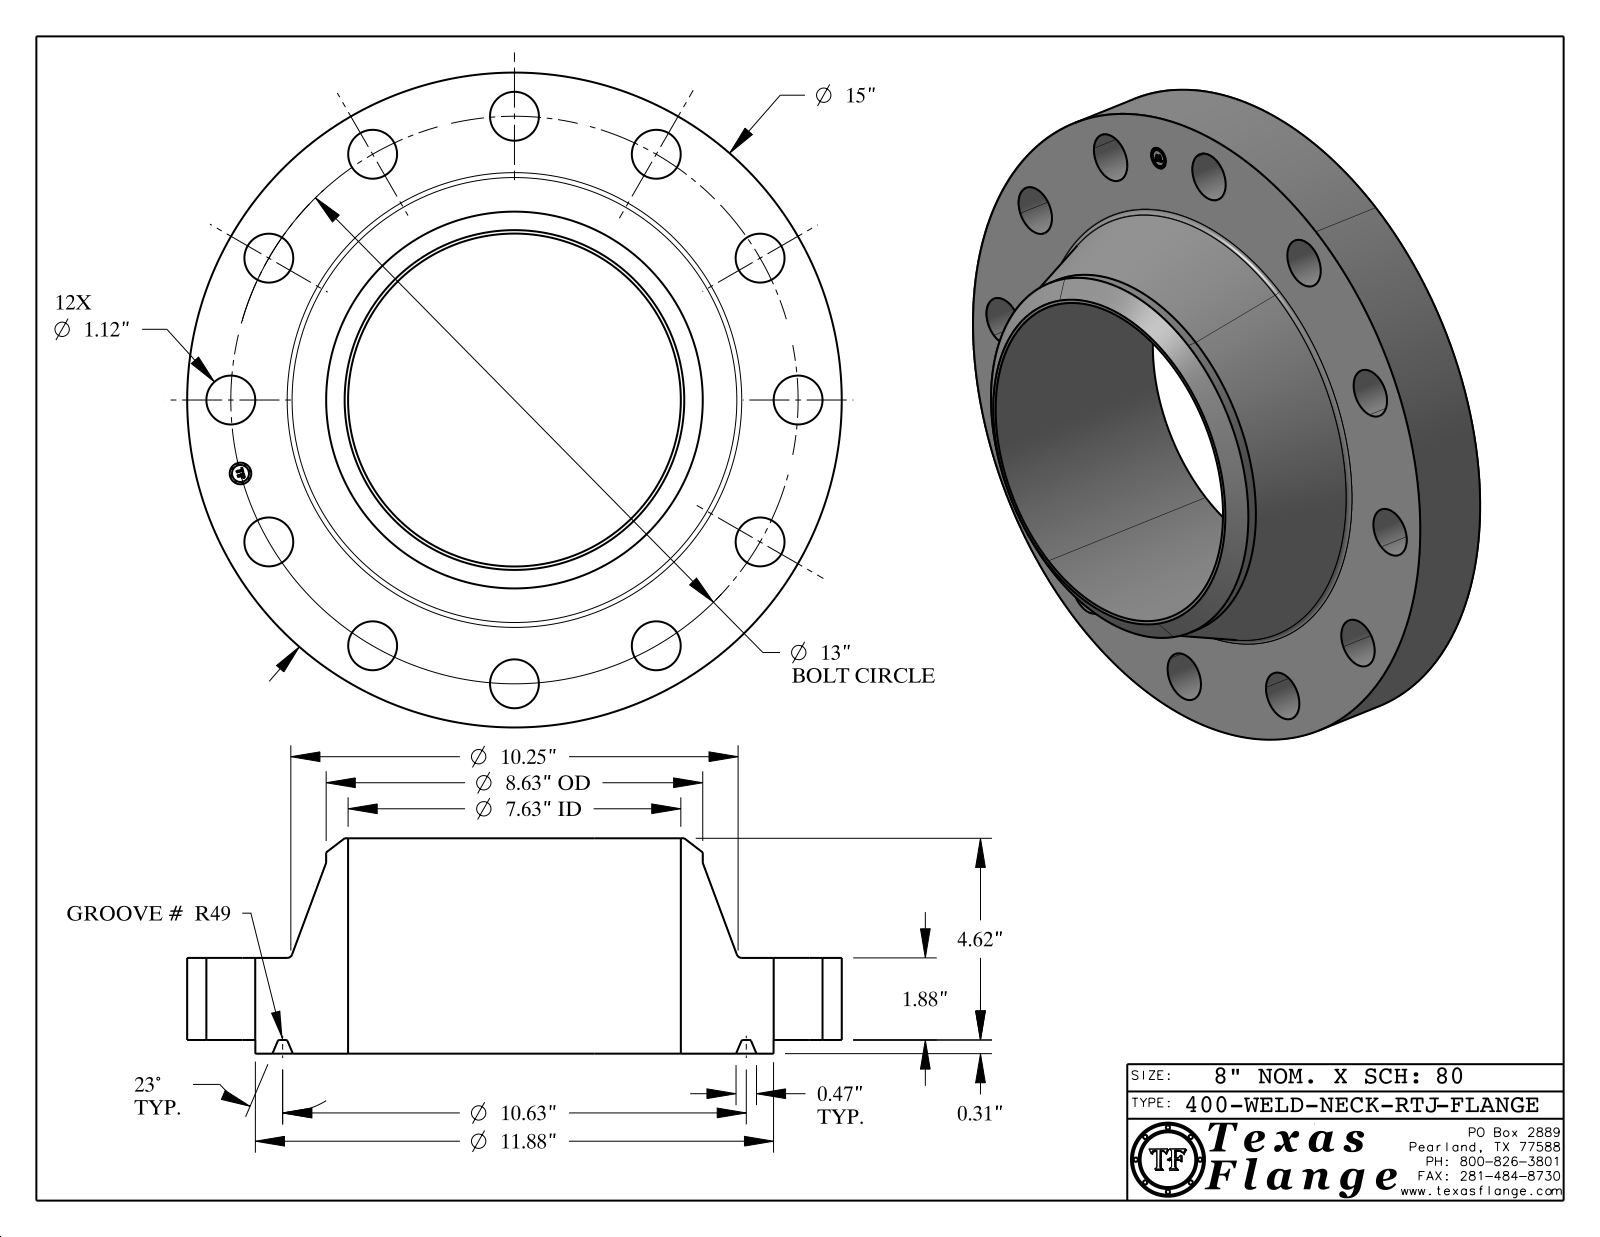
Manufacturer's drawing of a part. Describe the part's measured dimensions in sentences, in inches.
The part is named "400-WELD-NECK-RTJ". Its 3-D file was written by "CATIA V5 STEP AP214 (AUTOMOTIVE_DESIGN)". It is 1 solid with 437 faces: 371 planar, 52 cylindrical and 14 other. Overall it measures 15 by 15 by 4.933 inches. Its volume is 299.8 cubic inches and its surface area 603.4 square inches. Round holes: 12 of diameter 1.12, 1 of diameter 0.495, 1 of diameter 7.625. Round bosses or shafts: 8 of diameter 0.03, 1 of diameter 15, 1 of diameter 11.875, 1 of diameter 8.63, 1 of diameter 0.39. The main face-to-face distances are 1.88, 0.313, 2.193, 4.933, 4.62, 2.74, 2.178, 1.865, 0.015, 2.755. The hole center spacings are 6.5, 3.365, 9.193, 11.258, 12.557, 13, 1.697, 4.975.
